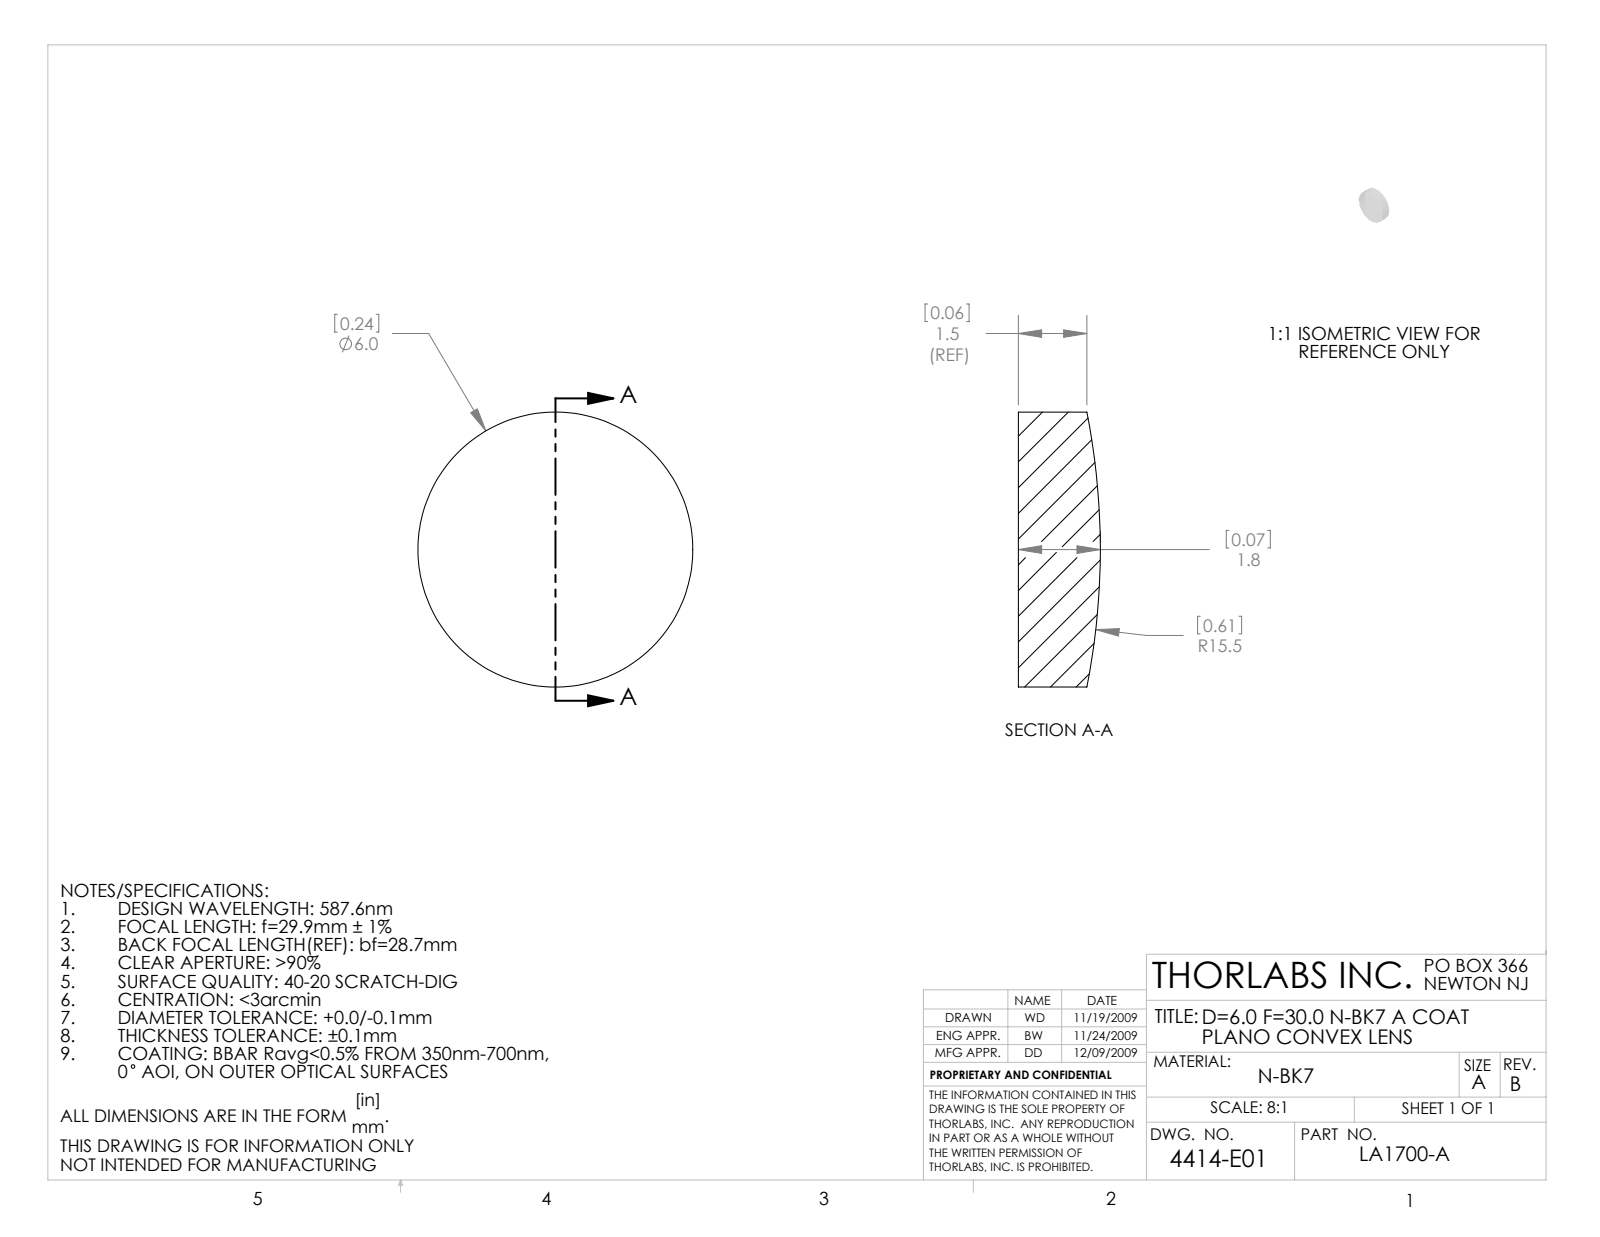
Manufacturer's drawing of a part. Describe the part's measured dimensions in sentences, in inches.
The part is named "4414-E0W". Its 3-D file was written by "SolidWorks 2009 (AUTOMOTIVE_DESIGN)". It is 1 solid with 5 faces: 1 planar, 2 cylindrical and 2 other. Overall it measures 0.236 by 0.236 by 0.07 inches. Its volume is 0.003 cubic inches and its surface area 0.13 square inches. Round bosses or shafts: 1 of diameter 0.236.
